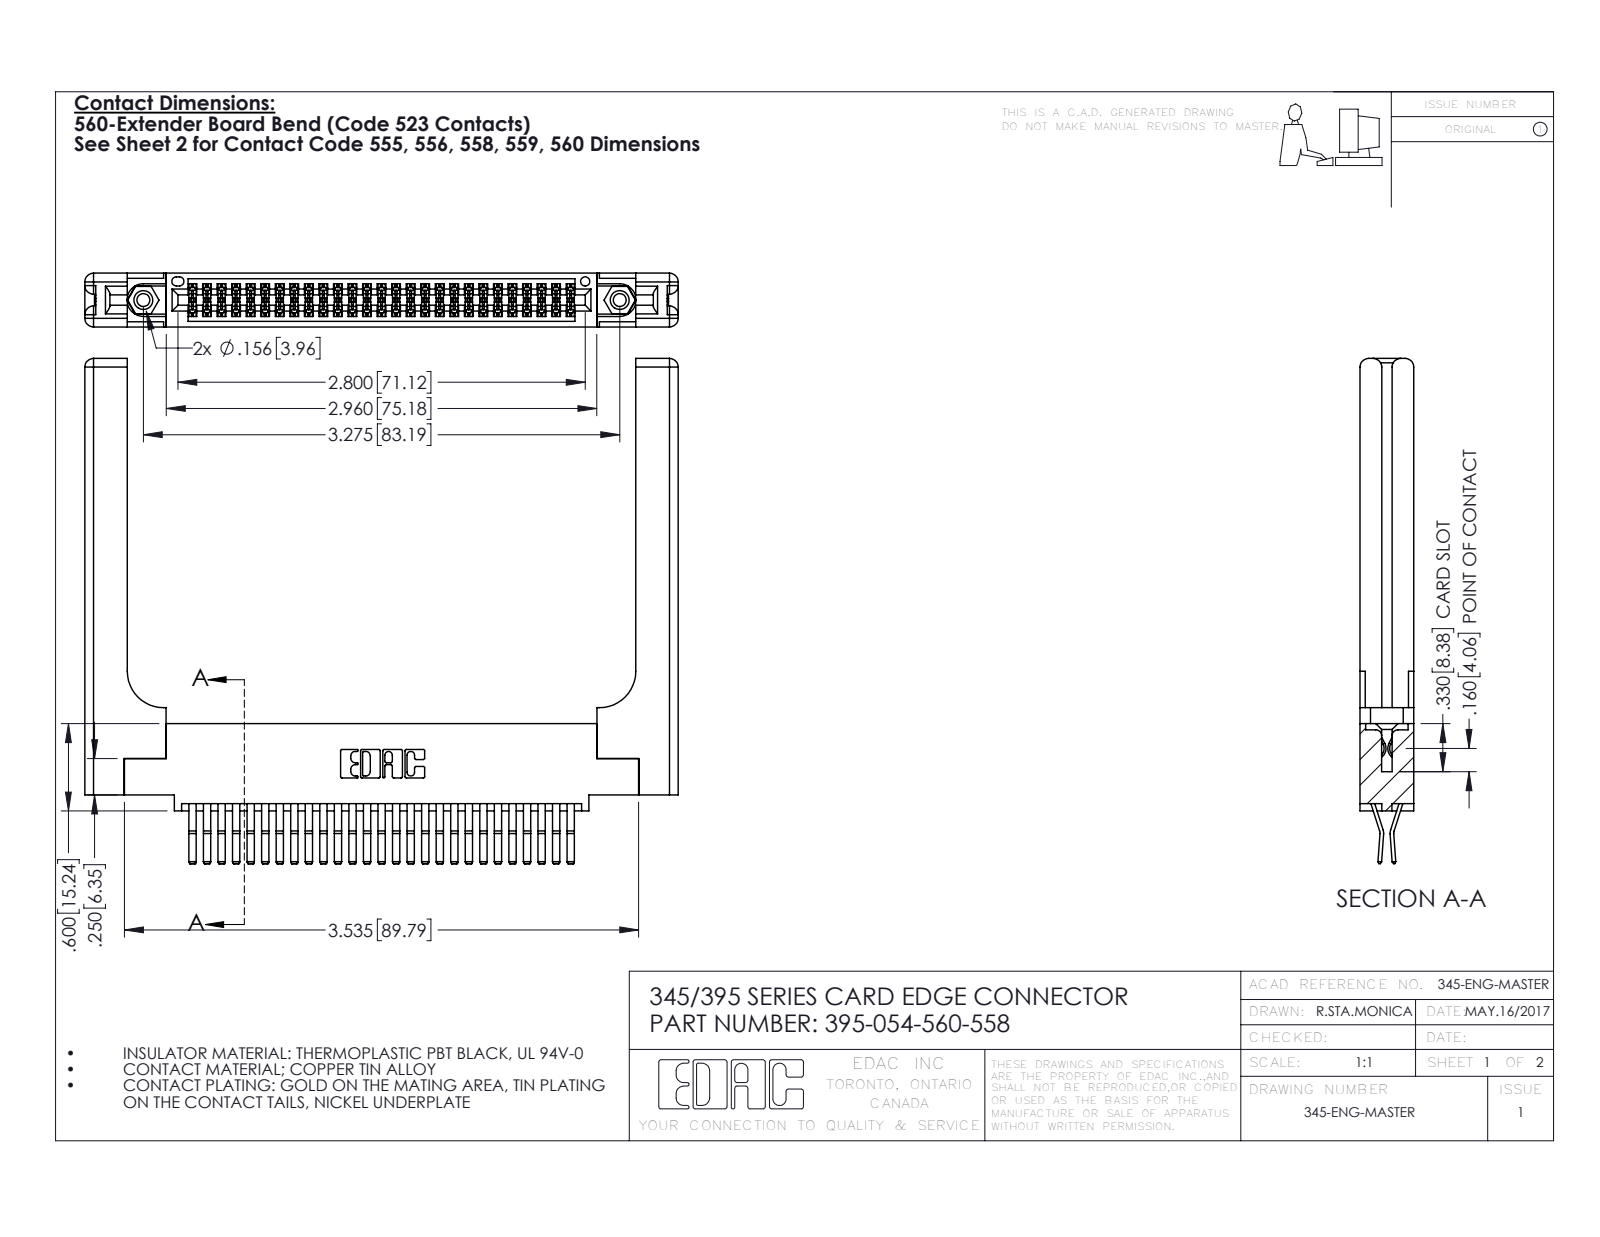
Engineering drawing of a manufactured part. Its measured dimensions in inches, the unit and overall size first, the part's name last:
Units: inches
Overall size (bounding box): 4.079 × 3.472 × 0.37
Round holes (diameter × count): ⌀0.089 ×2, ⌀0.125 ×2, ⌀0.156 ×2, ⌀0.064 ×1
Round bosses / shafts (diameter × count): ⌀0.155 ×2
Partial cylindrical surfaces — rounded edges, fillets, slot ends (radius × count): R0.006 ×81, R0.01 ×22, R0.06 ×16, R0.007 ×6, R0.031 ×6, R0.026 ×3, R0.01 ×2, R0.014 ×2
Main face-to-face distances: 0.37, 0.072, 0.298, 0.025, 0.225, 0.148, 0.15, 0.098, 0.272, 0.2
Hole centre spacings: 0.27, 3.04, 3.275
Volume: 1.14 in³ · Surface area: 32.33 in²
Bodies: 59 solids, 3194 faces (2014 planar, 1120 cylindrical, 60 other)
Part name (STEP PRODUCT): 345-250-001_345-250-001-102; 395-054-560-558; 345 Part_0.110 Offset - 0.156 Dia-TH; 345-292-001_560 Tail (+1 more)
STEP written by: SolidWorks 2016 (CONFIG_CONTROL_DESIGN)
